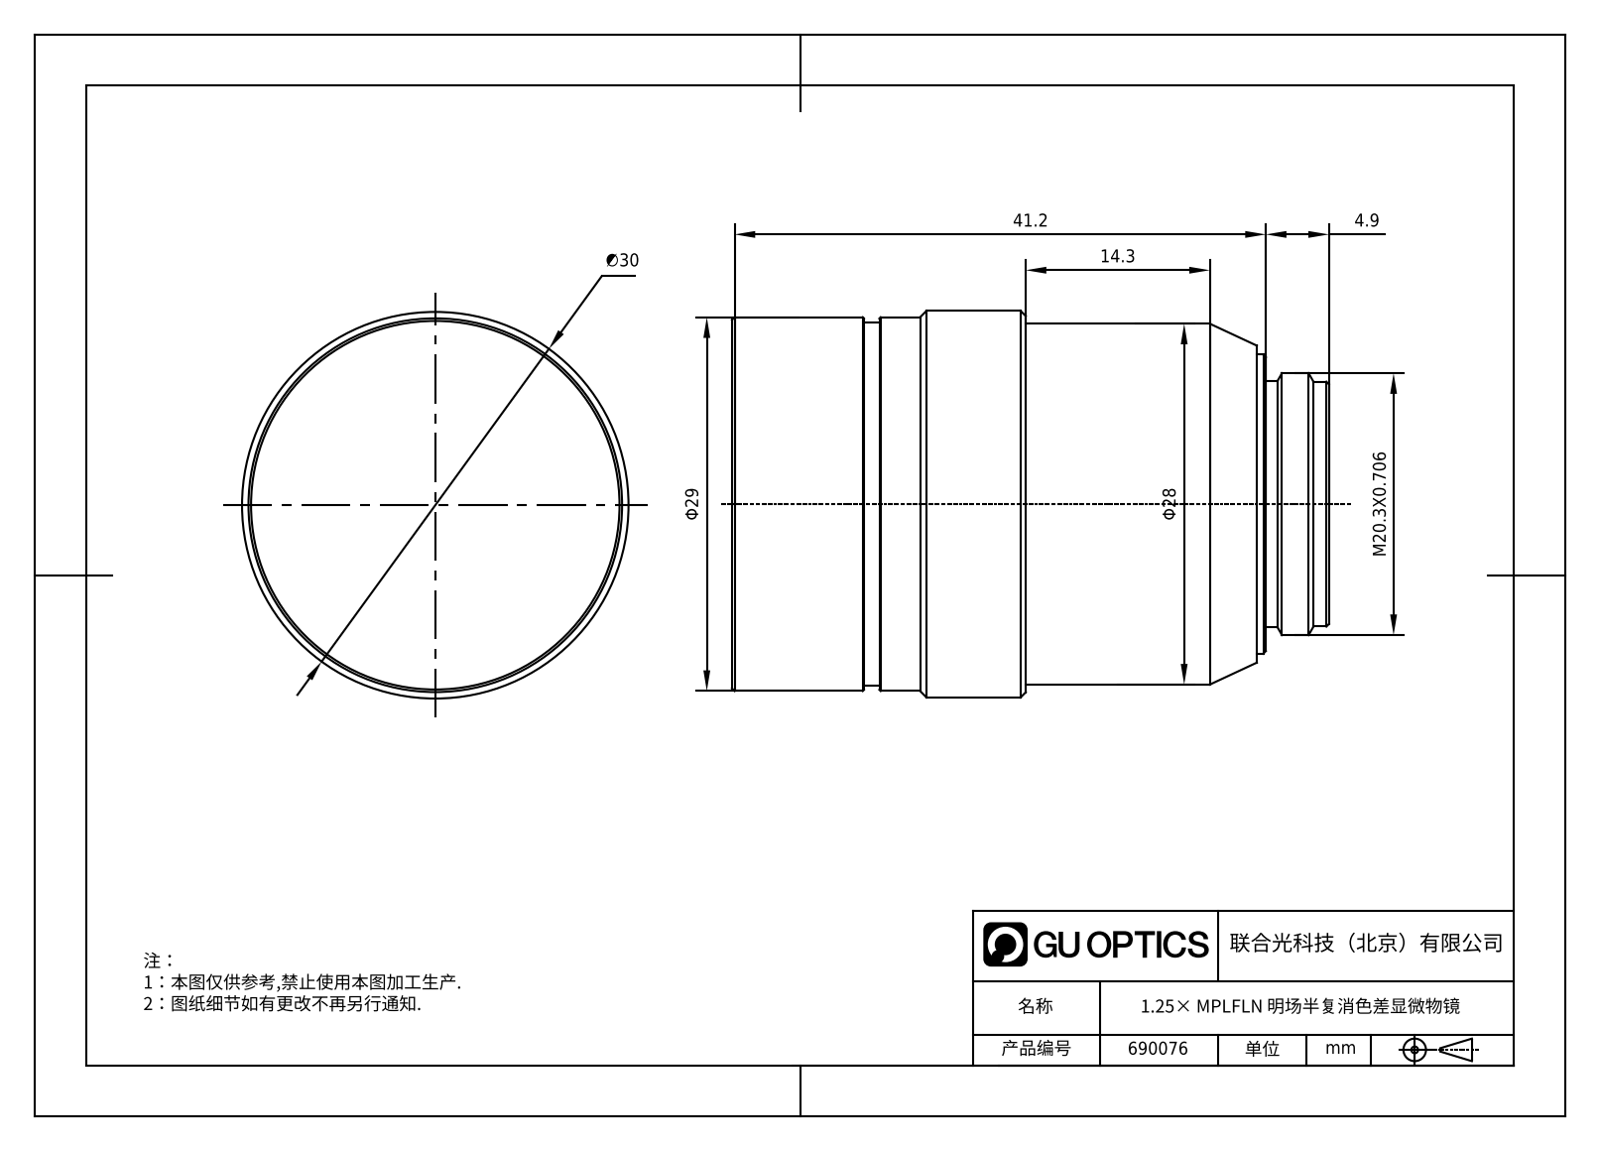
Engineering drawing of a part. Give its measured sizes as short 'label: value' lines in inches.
name: MPLFLN1.25X.stp; 690076.stp; 690076
written by: SolidWorks 2020 (CONFIG_CONTROL_DESIGN)
unit: in
bodies: 1 solid, 45 faces (7 planar, 18 cylindrical, 20 other)
size: 1.824 × 1.181 × 1.181
volume: 1.705 in³; area: 8.283 in²
bosses: 1× ⌀1.181, 1× ⌀1.142, 1× ⌀1.11, 1× ⌀1.102, 1× ⌀0.913, 1× ⌀0.8, 1× ⌀0.752, 1× ⌀0.748
face distances: 1.824, 1.631, 0.193, 0.898, 0.734, 0.927, 1.604, 0.706, 0.028, 0.22
